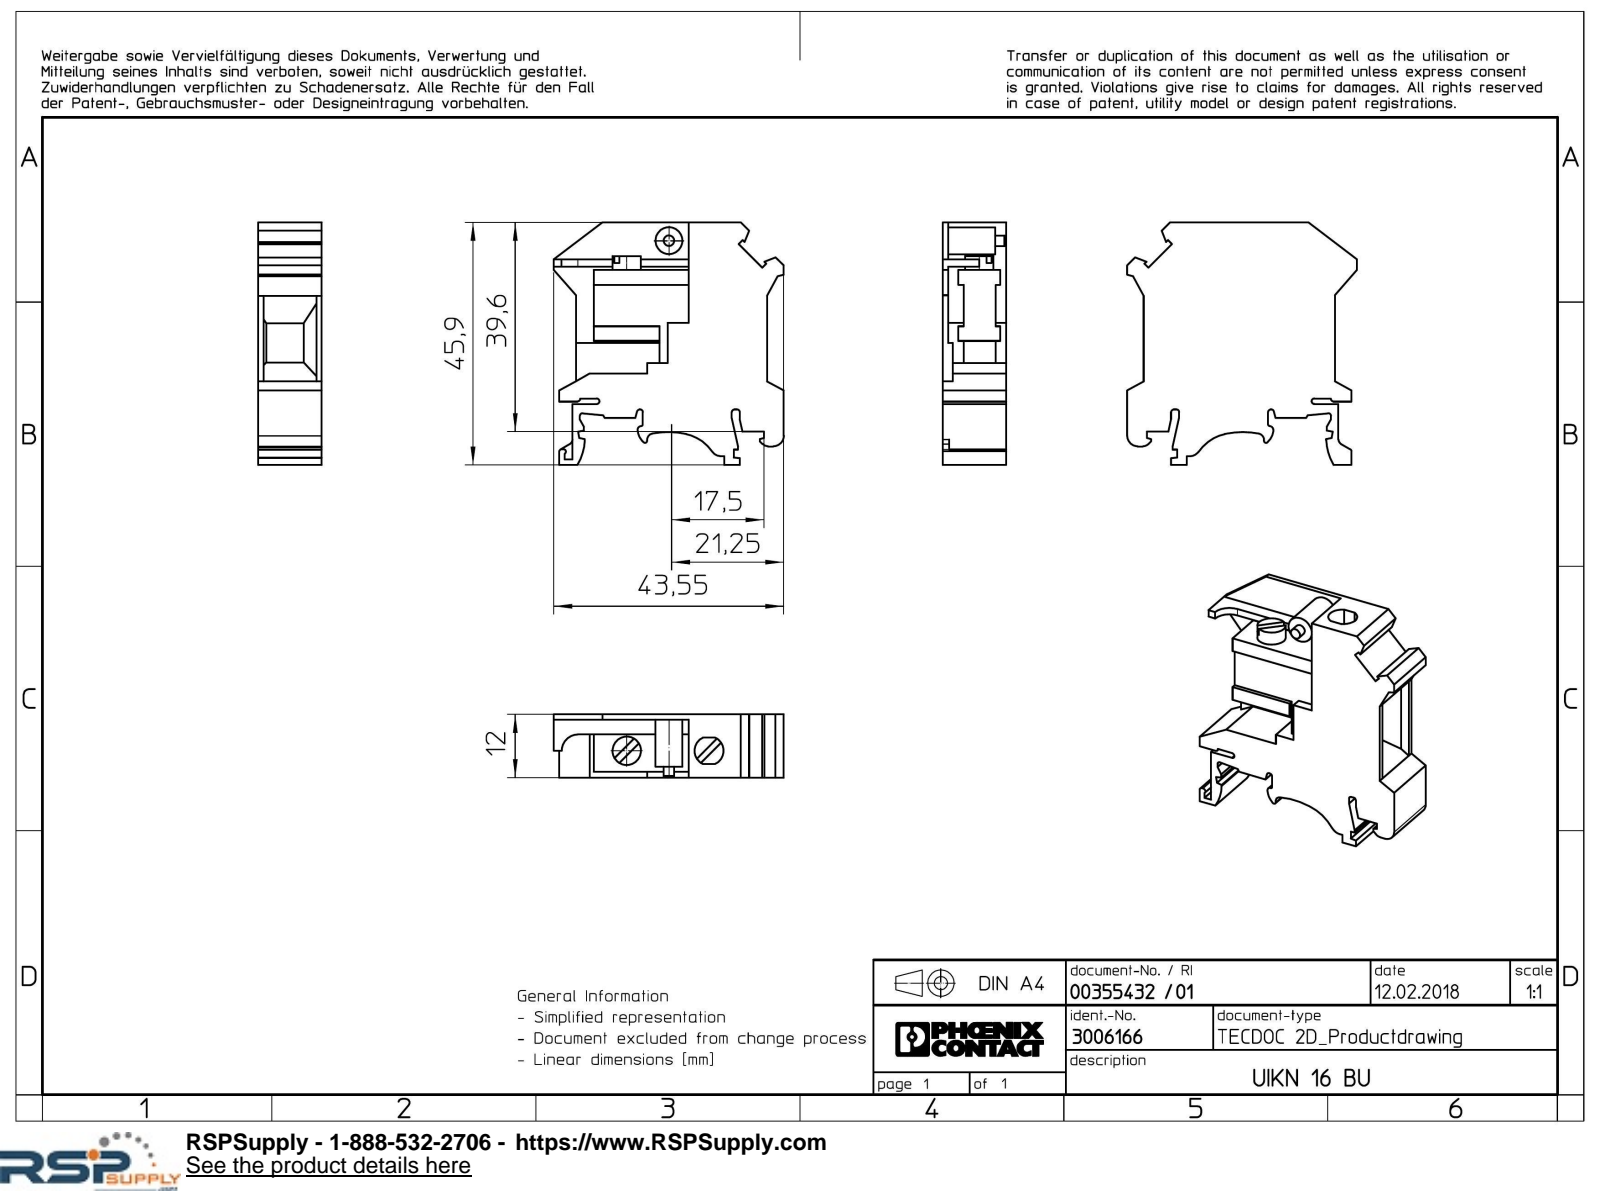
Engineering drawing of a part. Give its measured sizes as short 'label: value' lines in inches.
name: UIKN_16_BU-select
written by: Creo Elements/Direct Modeling 20.1A 29-Sep-2018 (C) Parametric Technology GmbH (AUTOMOTIVE_DESIGN)
unit: in
bodies: 1 solid, 157 faces (126 planar, 31 cylindrical, 0 other)
size: 1.807 × 1.715 × 0.472
volume: 0.746 in³; area: 11.67 in²
bosses: 1× ⌀0.213, 1× ⌀0.201, 1× ⌀0.079
rounds: 8× R0.02, 1× R0.012, 1× R0.016, 1× R0.02, 1× R0.021, 1× R0.028, 1× R0.039, 1× R0.047
face distances: 0.472, 0.039, 0.433, 0.077, 0.116, 0.709, 0.356, 0.317, 0.28, 0.083
